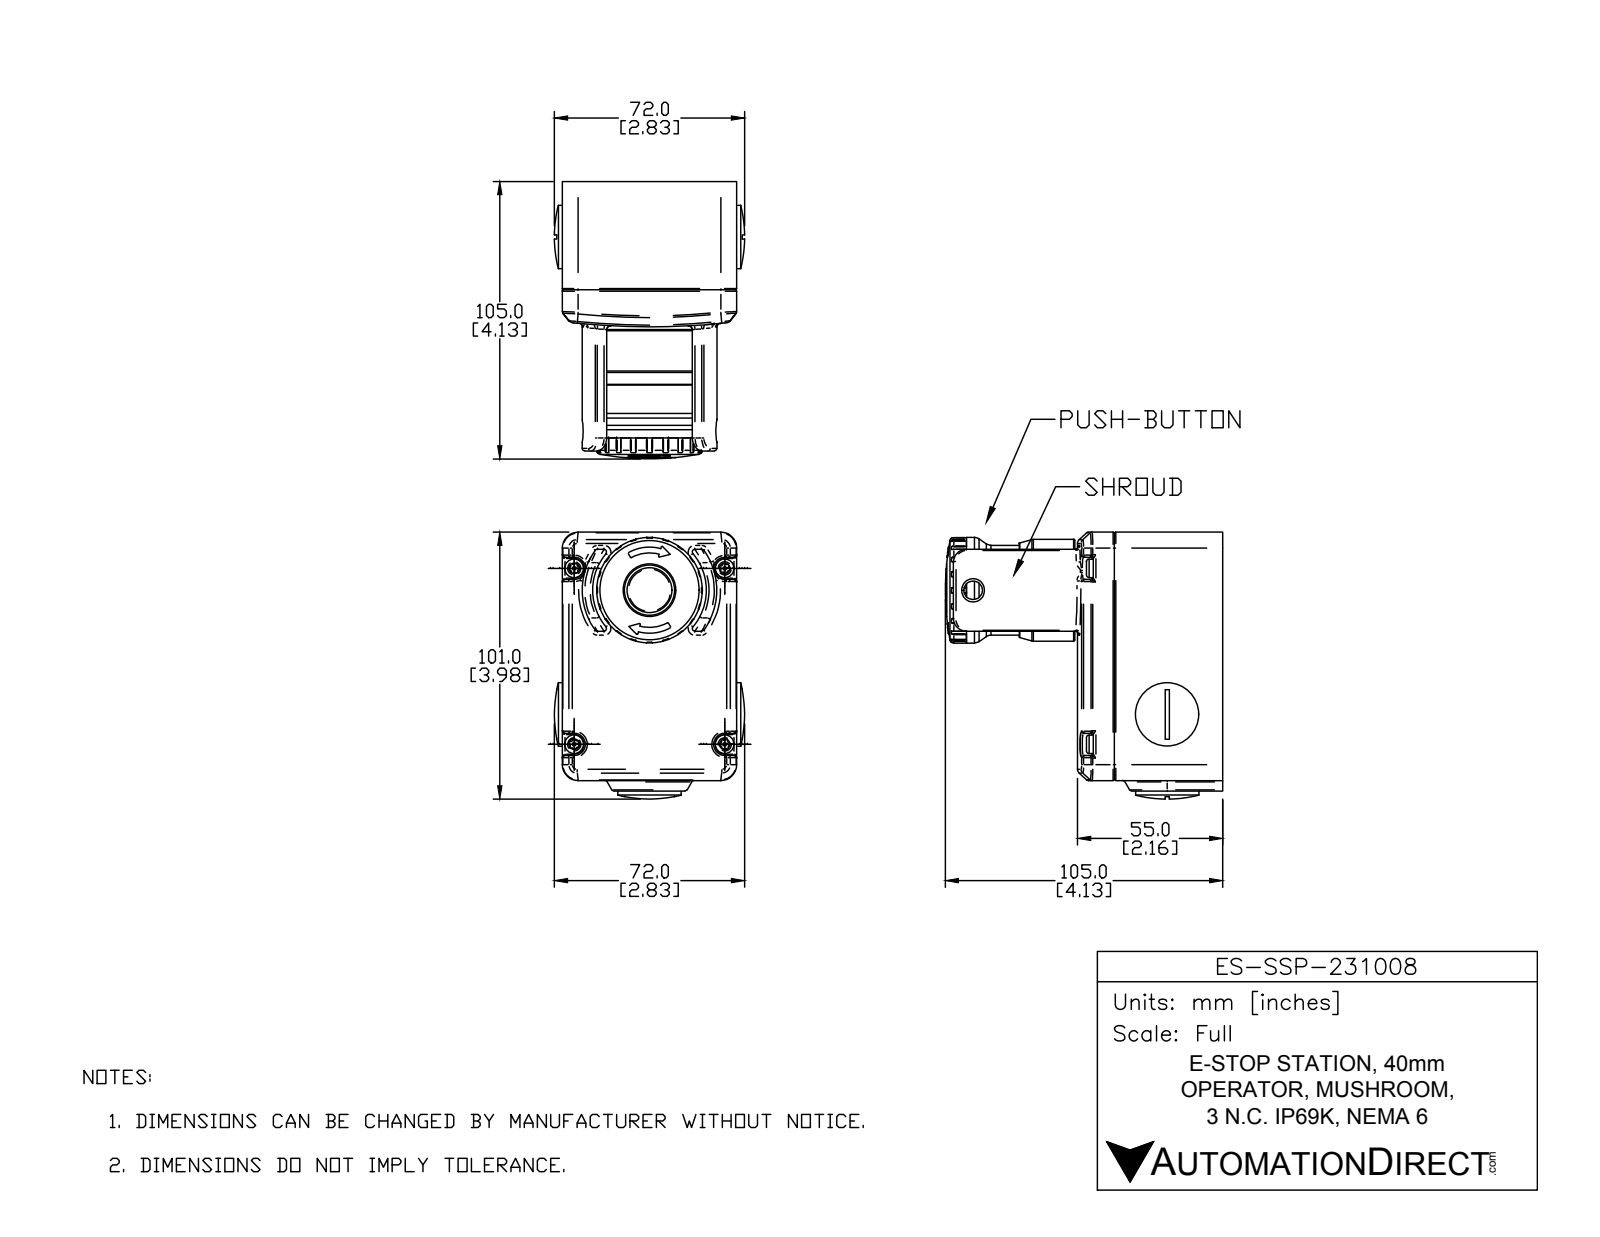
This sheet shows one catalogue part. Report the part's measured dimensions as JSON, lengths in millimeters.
{"part_name": "ES-SSP-231008", "step_written_by": "SolidWorks 2016 (AUTOMOTIVE_DESIGN)", "units": "millimeters", "bodies": {"solids": 10, "faces": 751, "planar": 219, "cylindrical": 276, "other": 256}, "overall_size": [105, 81.98, 70], "volume_mm3": 296547, "surface_area_mm2": 57744, "round_holes": [[4.4, 4], [7, 1], [31.1, 1], [37, 1]], "round_bosses_or_shafts": [[7, 4], [1, 4], [40, 1], [38.6, 1], [34, 1], [32, 1], [24, 1]], "partial_cylinders_radius": [[0.1, 80], [0.76, 24], [1, 18], [0.5, 14], [0.2, 4], [4.2, 4], [6, 4], [2, 2]], "face_to_face_distances": [41, 5, 71, 70, 56, 15, 76, 66, 56.8, 15.8], "hole_center_spacings": [31.38, 49.93, 54, 58, 79.25]}
